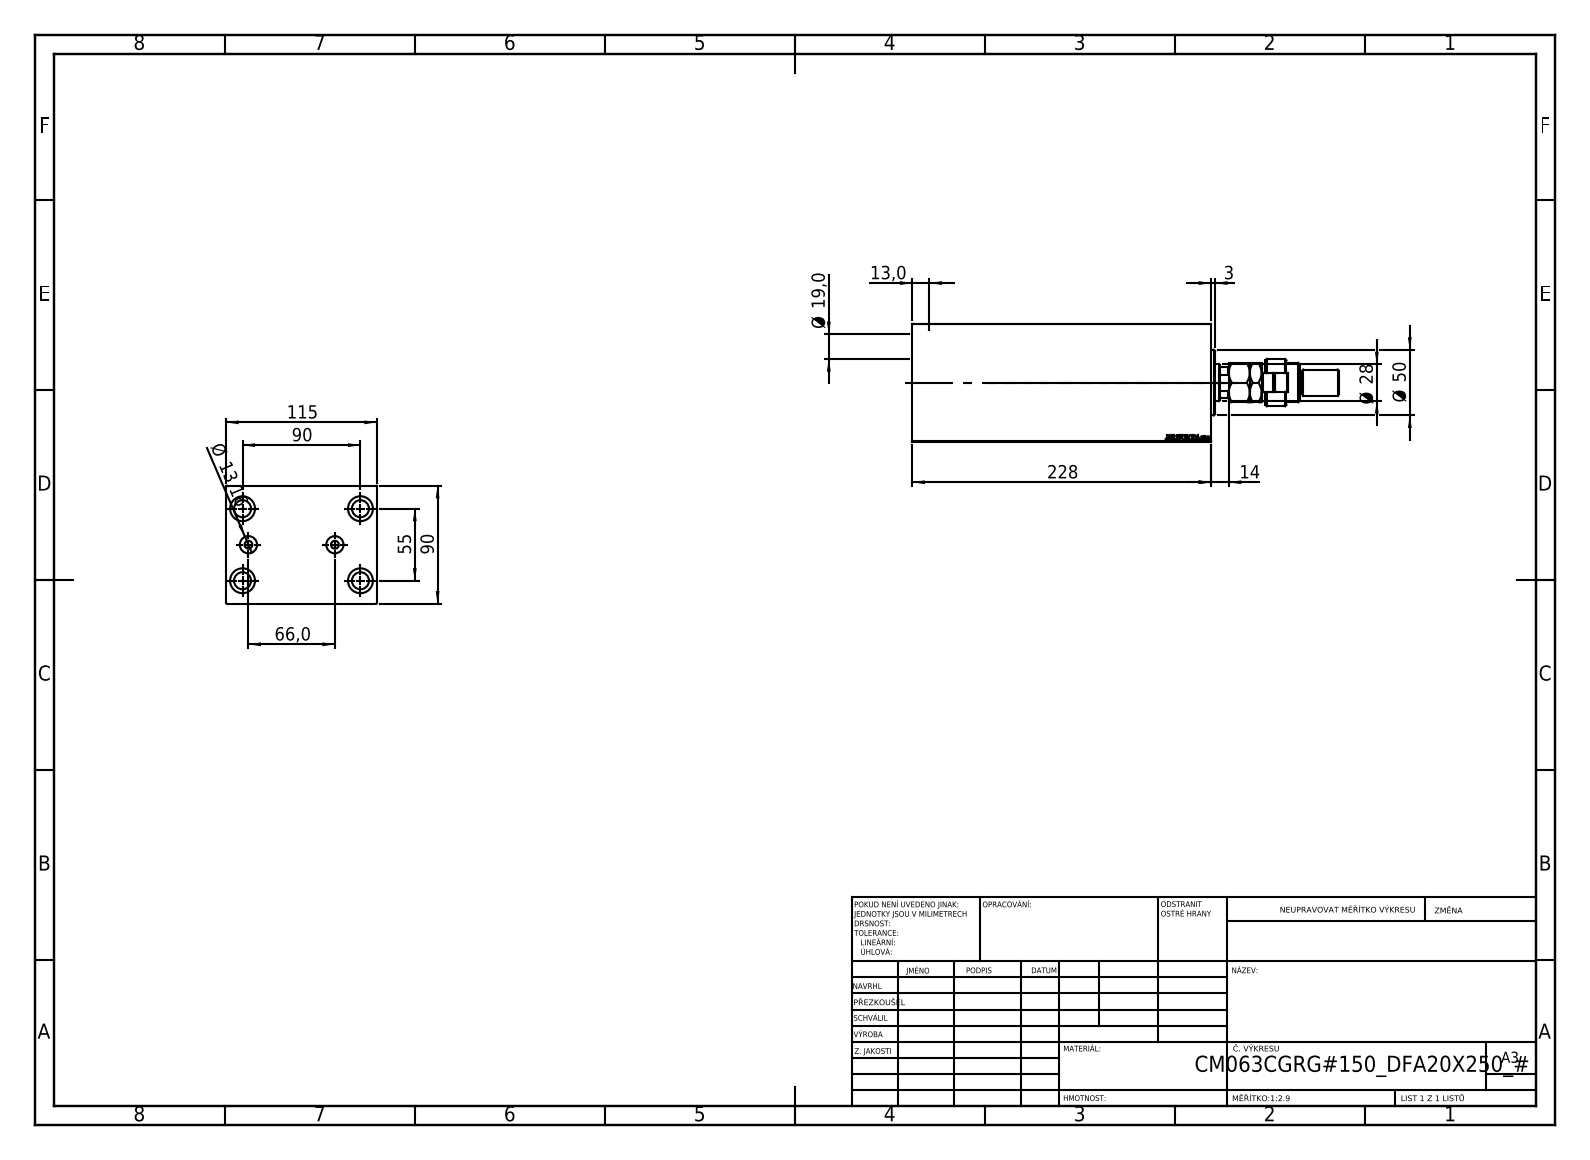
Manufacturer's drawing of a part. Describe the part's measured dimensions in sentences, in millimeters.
The part is named "MFA; V450CM_C_Body; V450CM_VC_B; FEMALE_PART_FOR_DFA (+1 more)". Its 3-D file was written by "SolidWorks 2019 (CONFIG_CONTROL_DESIGN)". It is 5 solids with 945 faces: 436 planar, 71 cylindrical and 438 other. Overall it measures 325.5 by 115 by 90 millimeters. Its volume is 1 892 000 cubic millimeters and its surface area 256 253 square millimeters. Round holes: 4 of diameter 13, 4 of diameter 19, 2 of diameter 6, 2 of diameter 13.16, 1 of diameter 18.5, 1 of diameter 28, 1 of diameter 31.5, 1 of diameter 63, 1 of diameter 65, 1 of diameter 72. Round bosses or shafts: 1 of diameter 50, 1 of diameter 36, 1 of diameter 30, 1 of diameter 22, 1 of diameter 20, 1 of diameter 18, 1 of diameter 14. Partial cylindrical surfaces (rounded edges, fillets, slot ends): 1 of radius 7.5, 1 of radius 12, 1 of radius 13.5. The main face-to-face distances are 90, 115, 228, 17.5, 210.5, 13.5, 197, 214.5, 64.5, 47. The hole center spacings are 52.74, 27.87, 33.71, 55, 75.67, 89.81, 90, 105.48.
